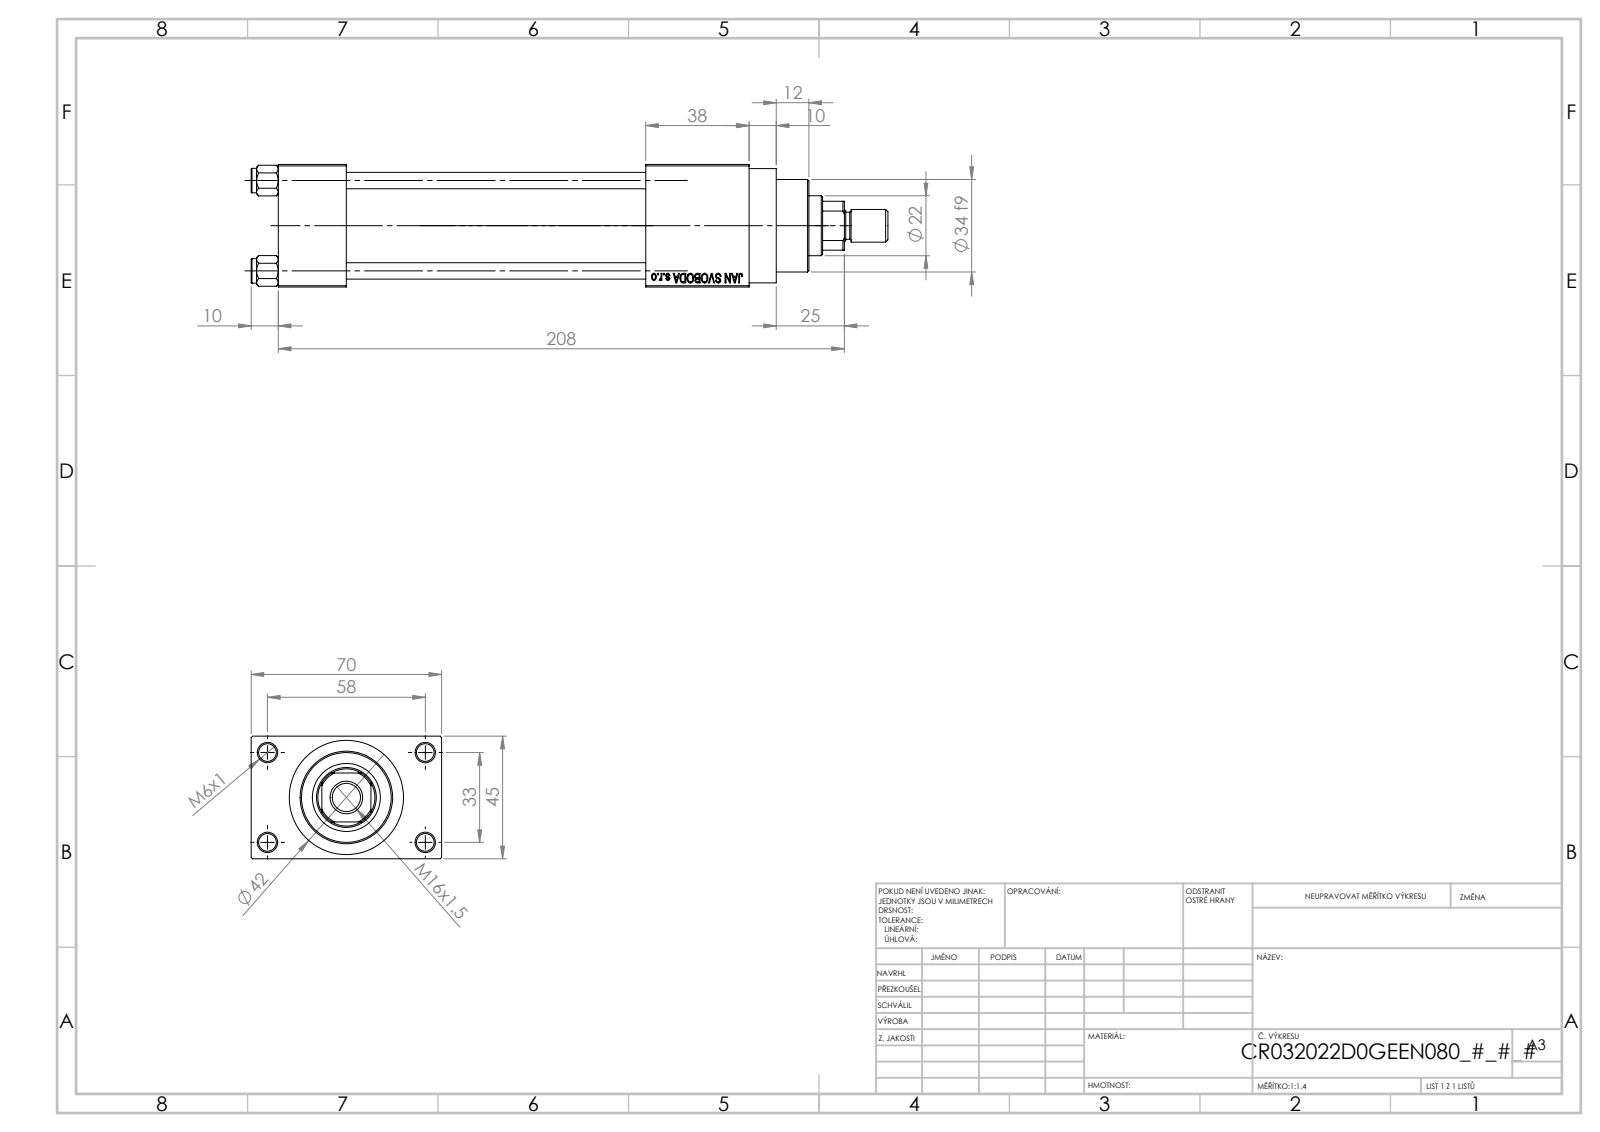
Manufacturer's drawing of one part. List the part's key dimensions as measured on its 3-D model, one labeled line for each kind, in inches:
Part name (STEP PRODUCT): ROD_END_E; V215CR_D_TYCINKA; V215CR_VCP_D; V215CR_D_Body (+2 more)
STEP written by: SolidWorks 2019 (CONFIG_CONTROL_DESIGN)
Units: inches
Bodies: 12 solids, 1117 faces (500 planar, 93 cylindrical, 524 other)
Overall size (bounding box): 9.213 × 2.756 × 1.772
Volume: 18.05 in³ · Surface area: 158.4 in²
Round holes (diameter × count): ⌀0.236 ×4, ⌀0.256 ×4, ⌀0.276 ×2, ⌀0.518 ×2, ⌀0.787 ×2, ⌀0.413 ×1, ⌀0.866 ×1, ⌀0.945 ×1, ⌀0.984 ×1, ⌀1.26 ×1, ⌀1.299 ×1
Round bosses / shafts (diameter × count): ⌀0.354 ×4, ⌀1.654 ×1, ⌀1.496 ×1, ⌀1.339 ×1, ⌀0.472 ×1, ⌀0.394 ×1
Partial cylindrical surfaces — rounded edges, fillets, slot ends (radius × count): R0.413 ×1
Main face-to-face distances: 1.772, 0.984, 0.492, 2.264, 4.331, 5.315, 5.827, 2.756, 1.496, 6.811
Hole centre spacings: 0.488, 0.924, 1.307, 1.314, 1.392, 1.795, 2.219, 1.299
